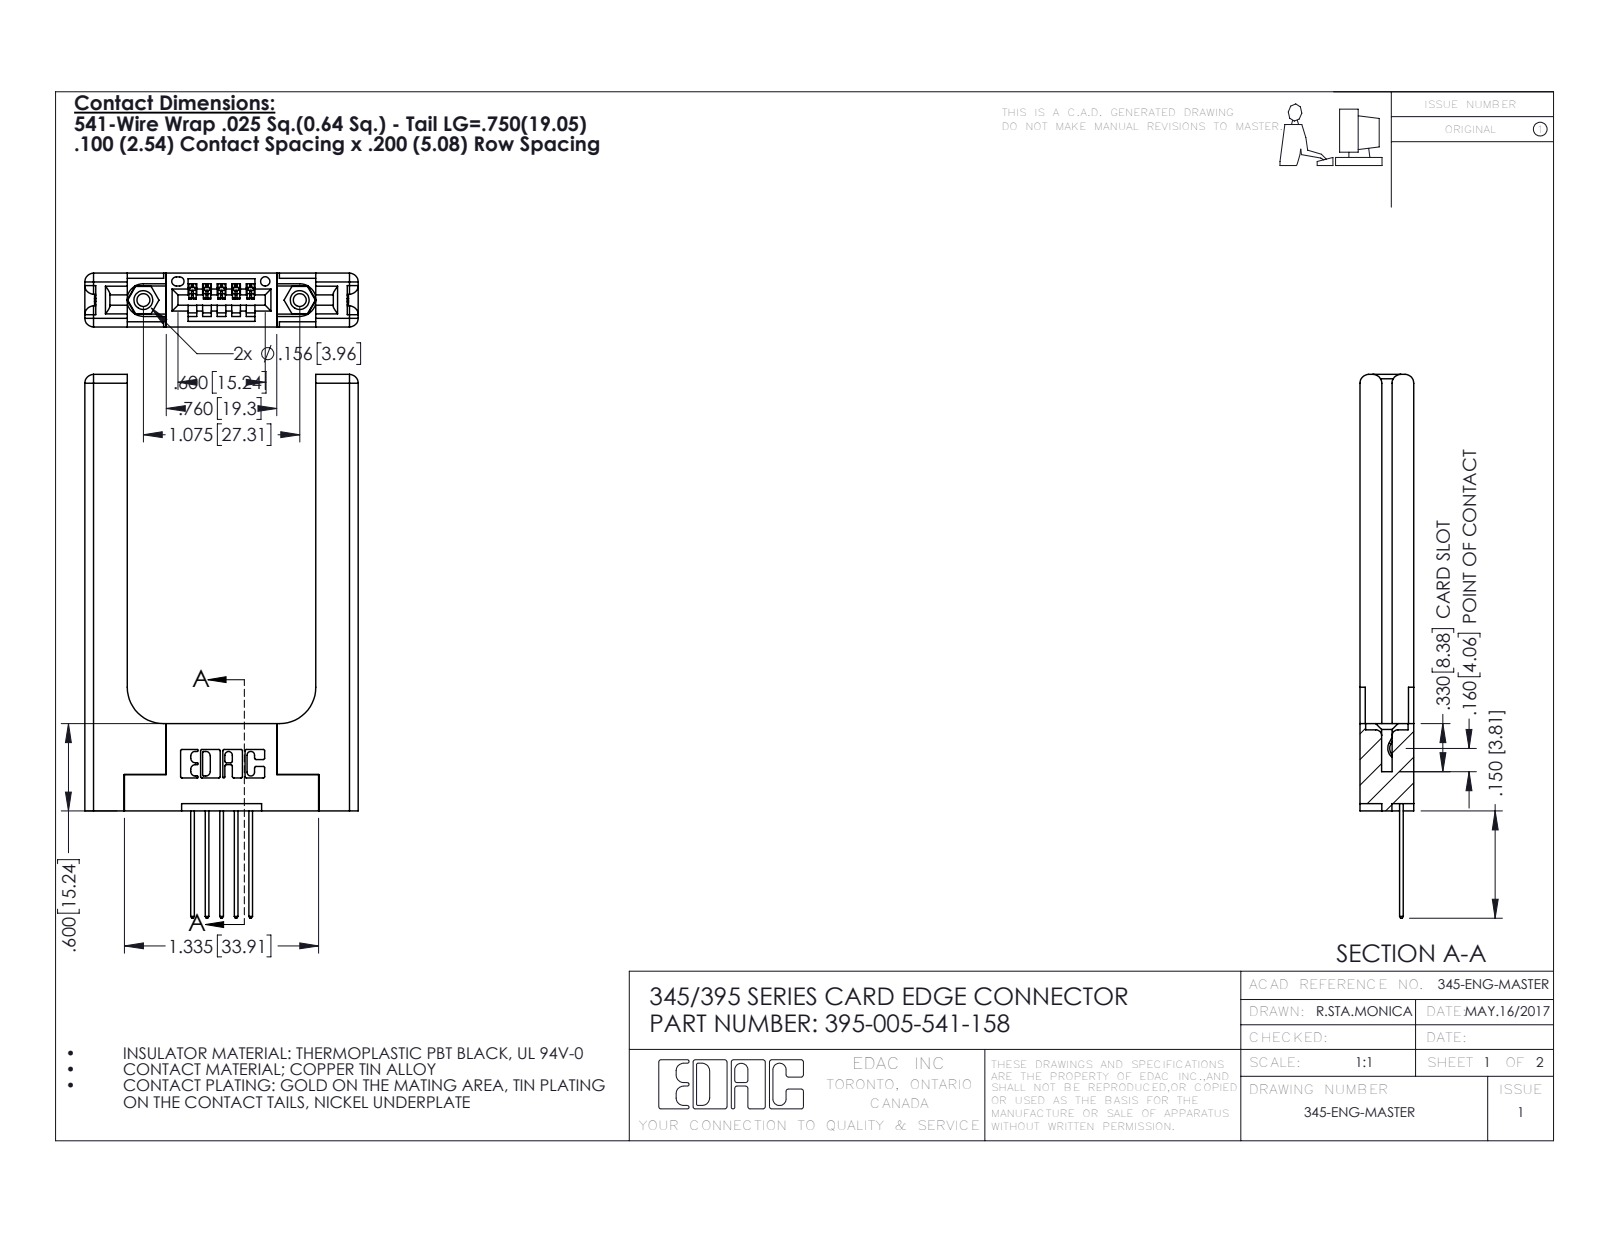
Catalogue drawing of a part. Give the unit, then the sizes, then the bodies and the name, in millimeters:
Units: millimetres
Overall size (bounding box): 94.9 × 47.7 × 9.4
Round holes (diameter × count): ⌀2.3 ×2, ⌀3.2 ×2, ⌀4 ×2, ⌀1.6 ×1
Round bosses / shafts (diameter × count): ⌀3.9 ×2
Partial cylindrical surfaces — rounded edges, fillets, slot ends (radius × count): R0.3 ×22, R1.5 ×16, R0.2 ×10, R0.3 ×10, R0.2 ×6, R0.8 ×6, R0.7 ×3, R0.8 ×2
Main face-to-face distances: 9.4, 3.8, 5.6, 1.8, 32.9, 2, 3.8, 7.6, 1.8, 5.1
Hole centre spacings: 6.9, 21.5, 27.3
Volume: 12 700 mm³ · Surface area: 10 540 mm²
Bodies: 10 solids, 672 faces (428 planar, 184 cylindrical, 60 other)
Part name (STEP PRODUCT): 395-005-541-158; 345 Part_Flush Mounting Lugs - 0.156 Dia-TH; 345-250-001_345-250-001-102; 345-292-001_345-293-141 (+1 more)
STEP written by: SolidWorks 2016 (CONFIG_CONTROL_DESIGN)
